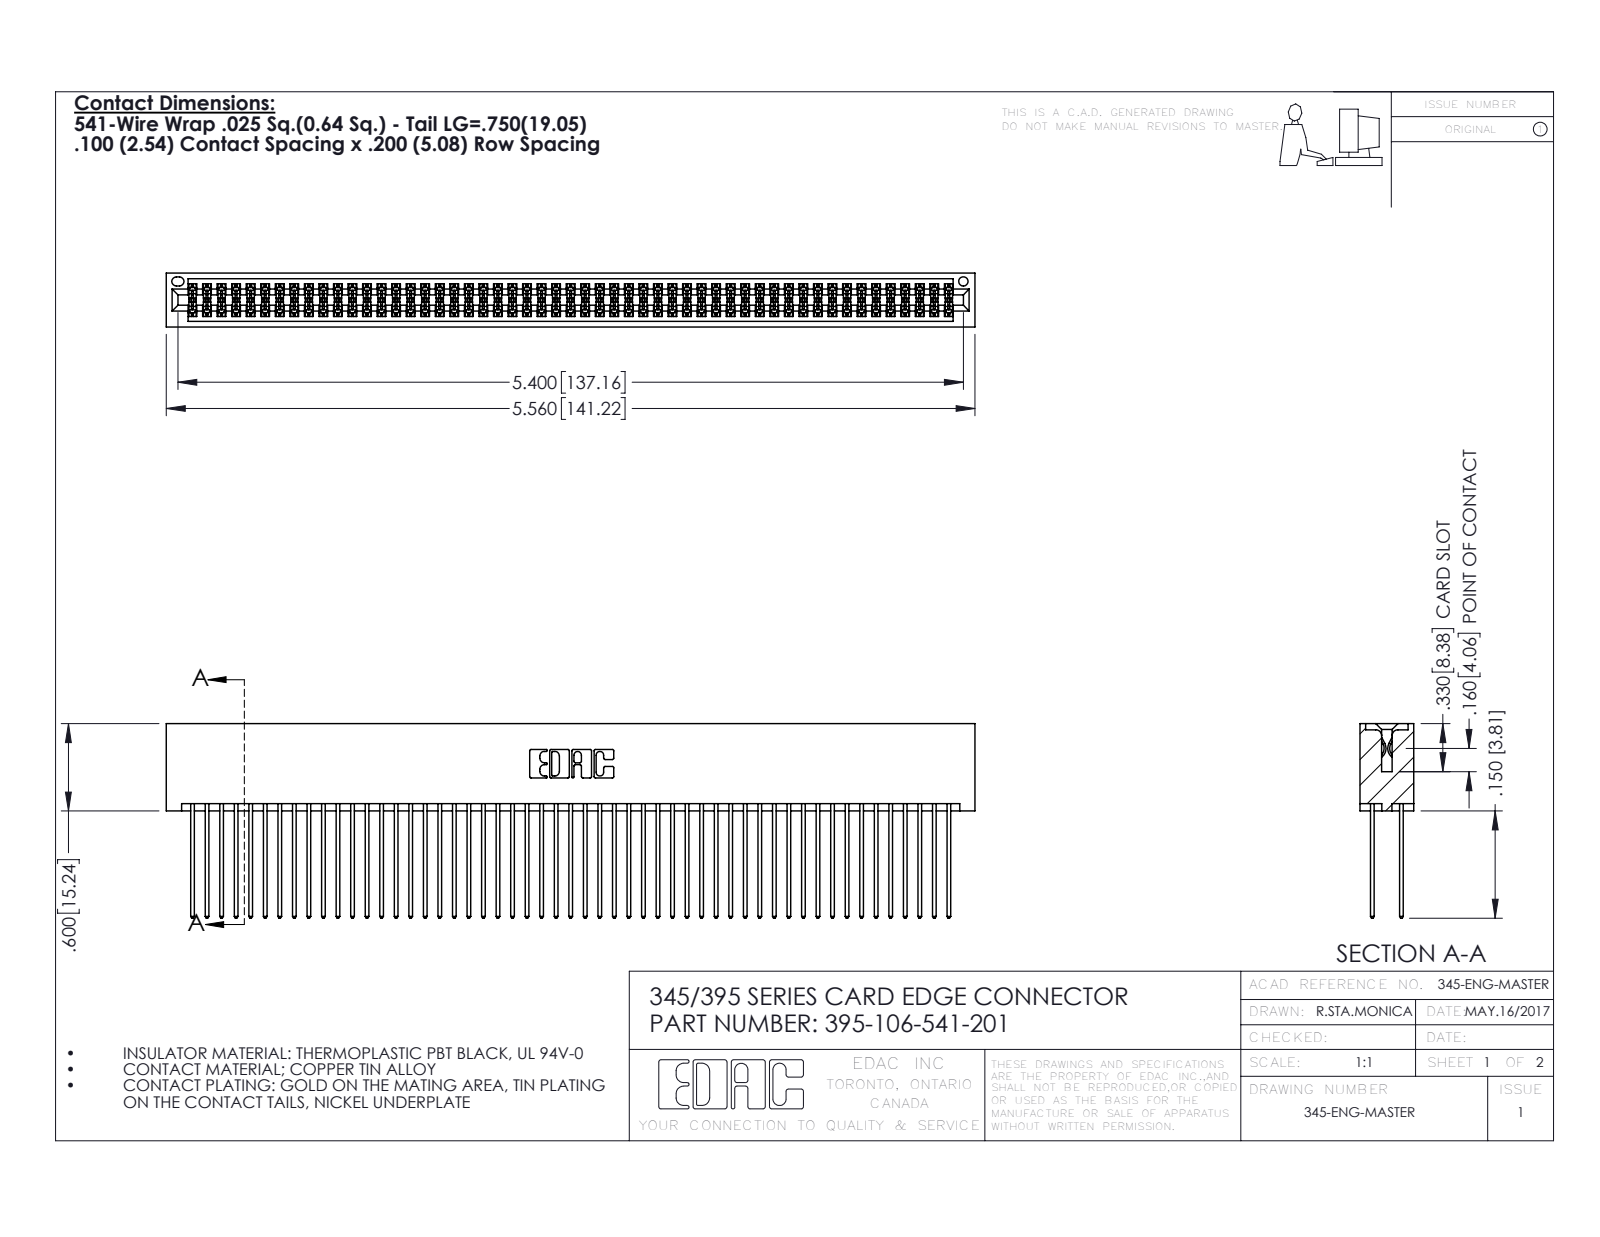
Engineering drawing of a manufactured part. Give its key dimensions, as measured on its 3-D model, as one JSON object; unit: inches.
{"part_name": "395-106-541-201; 345 Part_No Mounting Lugs; 345-292-001_345-293-141", "step_written_by": "SolidWorks 2016 (CONFIG_CONTROL_DESIGN)", "units": "inches", "bodies": {"solids": 107, "faces": 5418, "planar": 3574, "cylindrical": 1844, "other": 0}, "overall_size": [5.56, 1.337, 0.37], "volume_in3": 0.918, "surface_area_in2": 39.7, "round_holes": [[0.064, 1]], "partial_cylinders_radius": [[0.006, 159], [0.01, 106], [0.01, 22], [0.007, 6], [0.031, 6], [0.026, 3], [0.014, 2], [0.019, 2]], "face_to_face_distances": [0.298, 0.072, 0.2, 0.098, 0.272, 0.025, 0.225, 0.37, 0.175, 0.149]}
